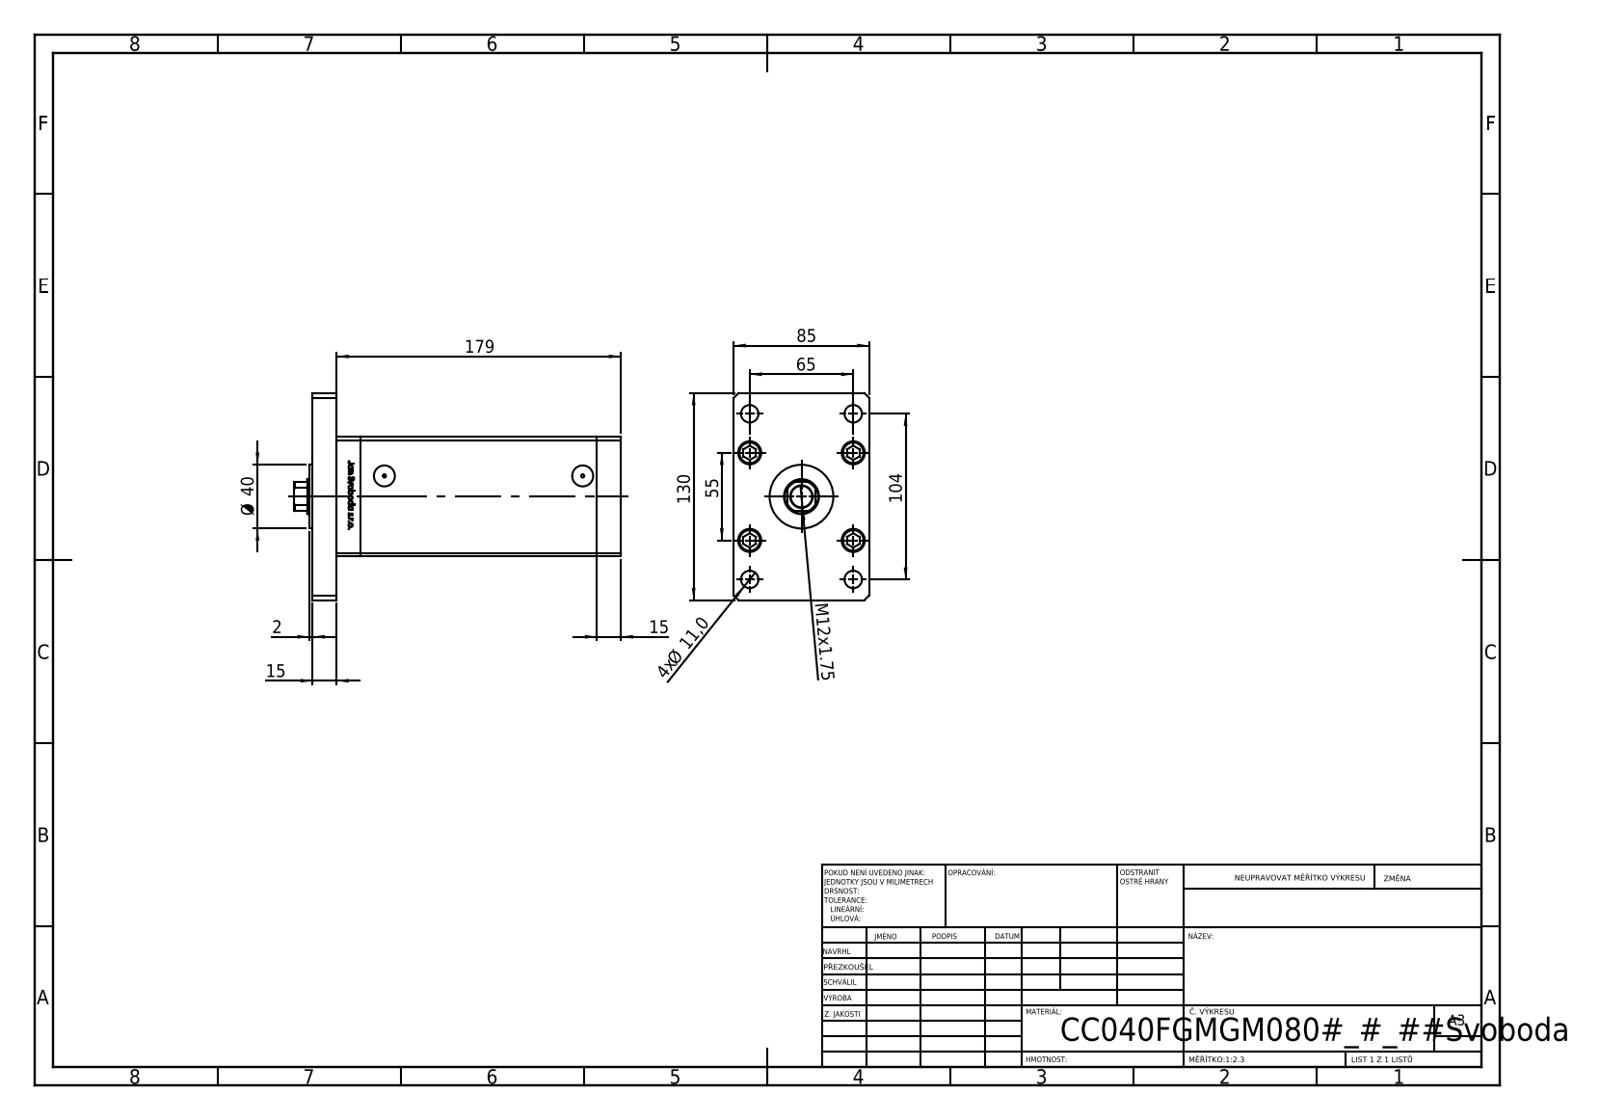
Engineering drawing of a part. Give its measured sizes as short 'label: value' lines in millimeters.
name: ALLEN BOLT; V220C BACK_F; V220C_FRONT_F; V220C_F (+2 more)
written by: SolidWorks 2019 (CONFIG_CONTROL_DESIGN)
unit: mm
bodies: 19 solids, 1308 faces (515 planar, 187 cylindrical, 606 other)
size: 205 × 130 × 85
volume: 1 165 000 mm³; area: 198 848 mm²
holes: 9× ⌀11, 5× ⌀15.5, 4× ⌀10, 4× ⌀14.5, 2× ⌀2, 2× ⌀13.16, 1× ⌀13.5, 1× ⌀22, 1× ⌀23.5
bosses: 9× ⌀8, 5× ⌀14.5, 1× ⌀40
rounds: 2× R0.93, 1× R10.5
face distances: 15, 85, 163.5, 178.5, 75, 148.5, 30, 193.5, 10.5, 27.5
hole spacings: 28, 24.5, 42.57, 61.32, 65, 69.46, 79.5, 102.69
